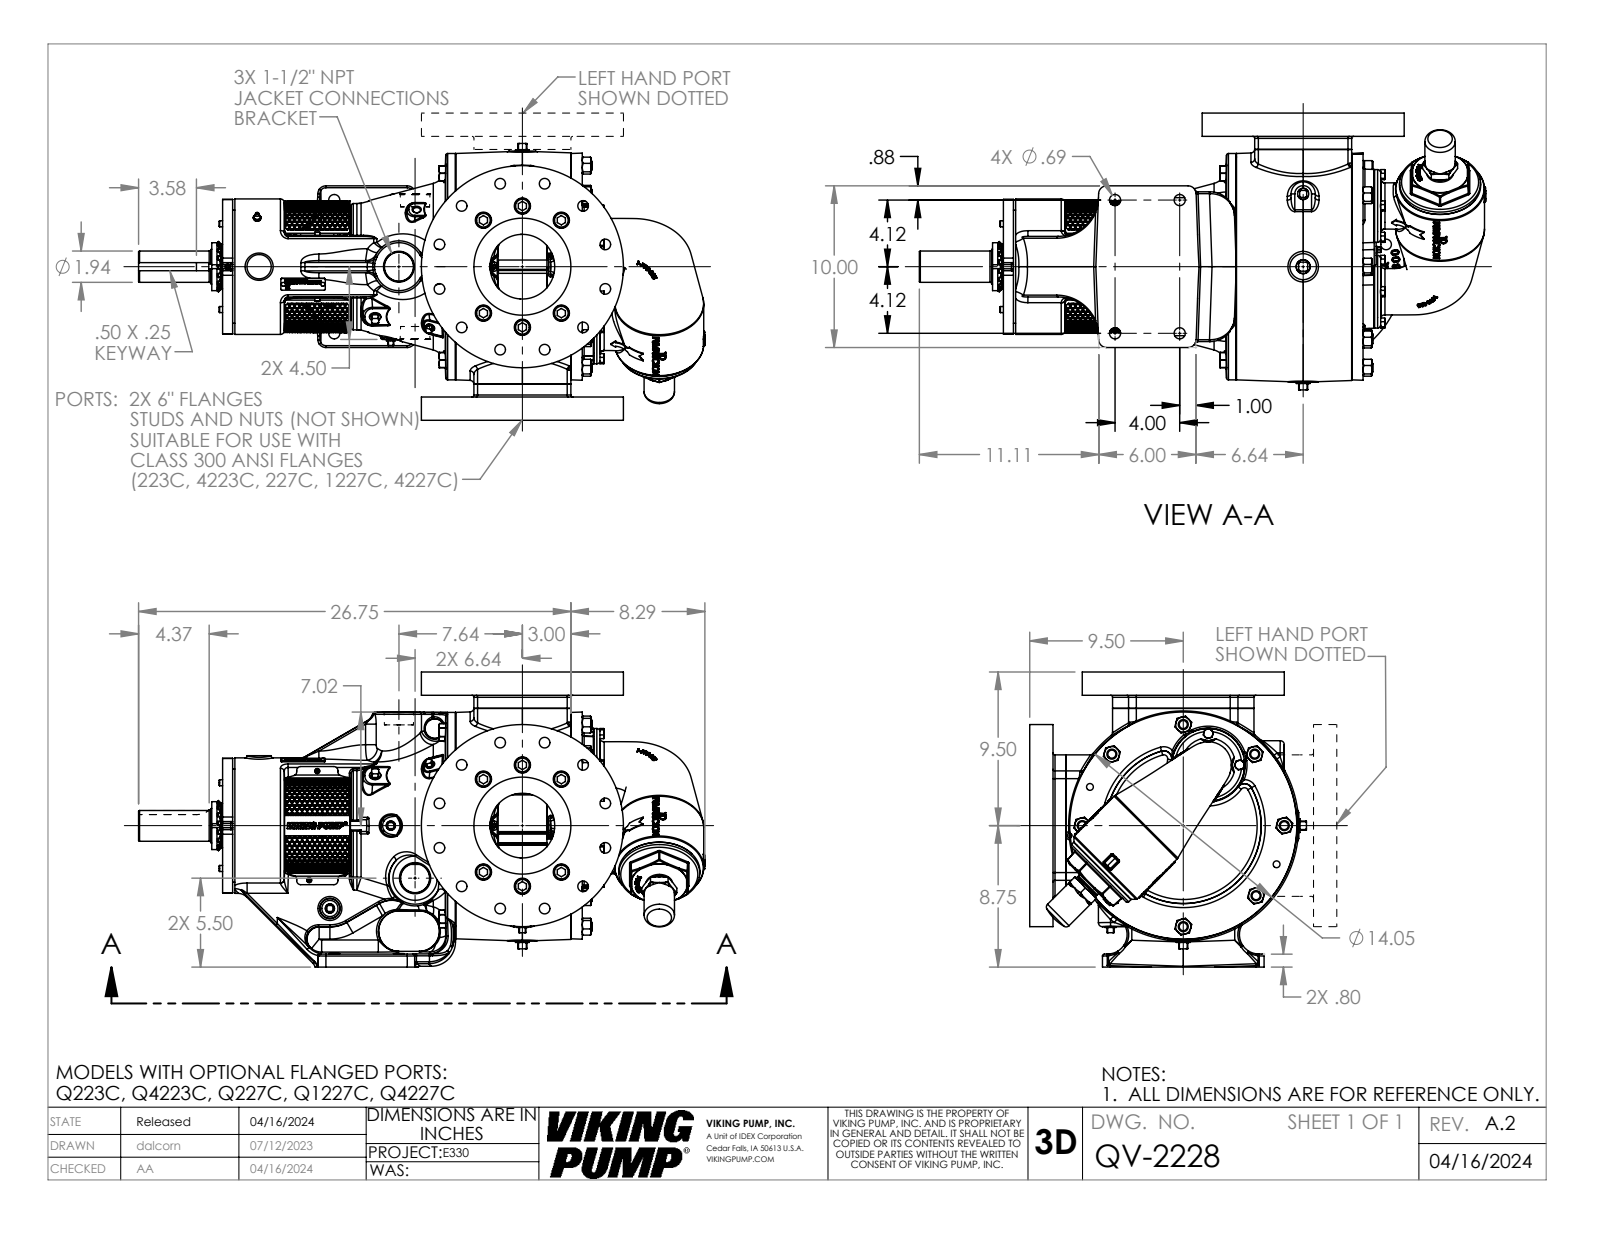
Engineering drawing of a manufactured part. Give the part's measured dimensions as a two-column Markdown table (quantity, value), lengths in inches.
| quantity | value |
| --- | --- |
| part name | QV-2228 |
| STEP written by | SolidWorks 2022 (AUTOMOTIVE_DESIGN) |
| units | inches |
| bodies | 1 solid, 4920 faces (1736 planar, 839 cylindrical, 2345 other) |
| overall size | 35.04 × 18.25 × 17.121 |
| volume | 2 790 in³ |
| surface area | 2 750 in² |
| round holes (diameter × count) | 0.656 × 36, 1 × 12, 0.25 × 9, 0.266 × 8, 0.406 × 8, 0.41 × 8, 1.157 × 8, 0.688 × 4, 0.159 × 2, 0.313 × 2, 0.33 × 2, 0.422 × 2 |
| round bosses / shafts (diameter × count) | 0.937 × 12, 0.625 × 12, 0.617 × 8, 0.375 × 8, 0.312 × 3, 0.19 × 3, 12.5 × 2, 4.5 × 2 |
| partial cylindrical surfaces (radius × count) | 0.12 × 52, 0.06 × 34, 0.5 × 22, 0.015 × 18, 0.092 × 18, 0.25 × 18, 0.07 × 16, 0.75 × 16 |
| main face-to-face distances | 1.44, 16.81, 18.25, 0.5, 3.75, 21.754, 22.254, 2.25, 18.004, 18.504 |
| hole center spacings | 5.313, 10.263, 3.75, 2.75, 9.202, 2.079, 7.513, 1.61 |
